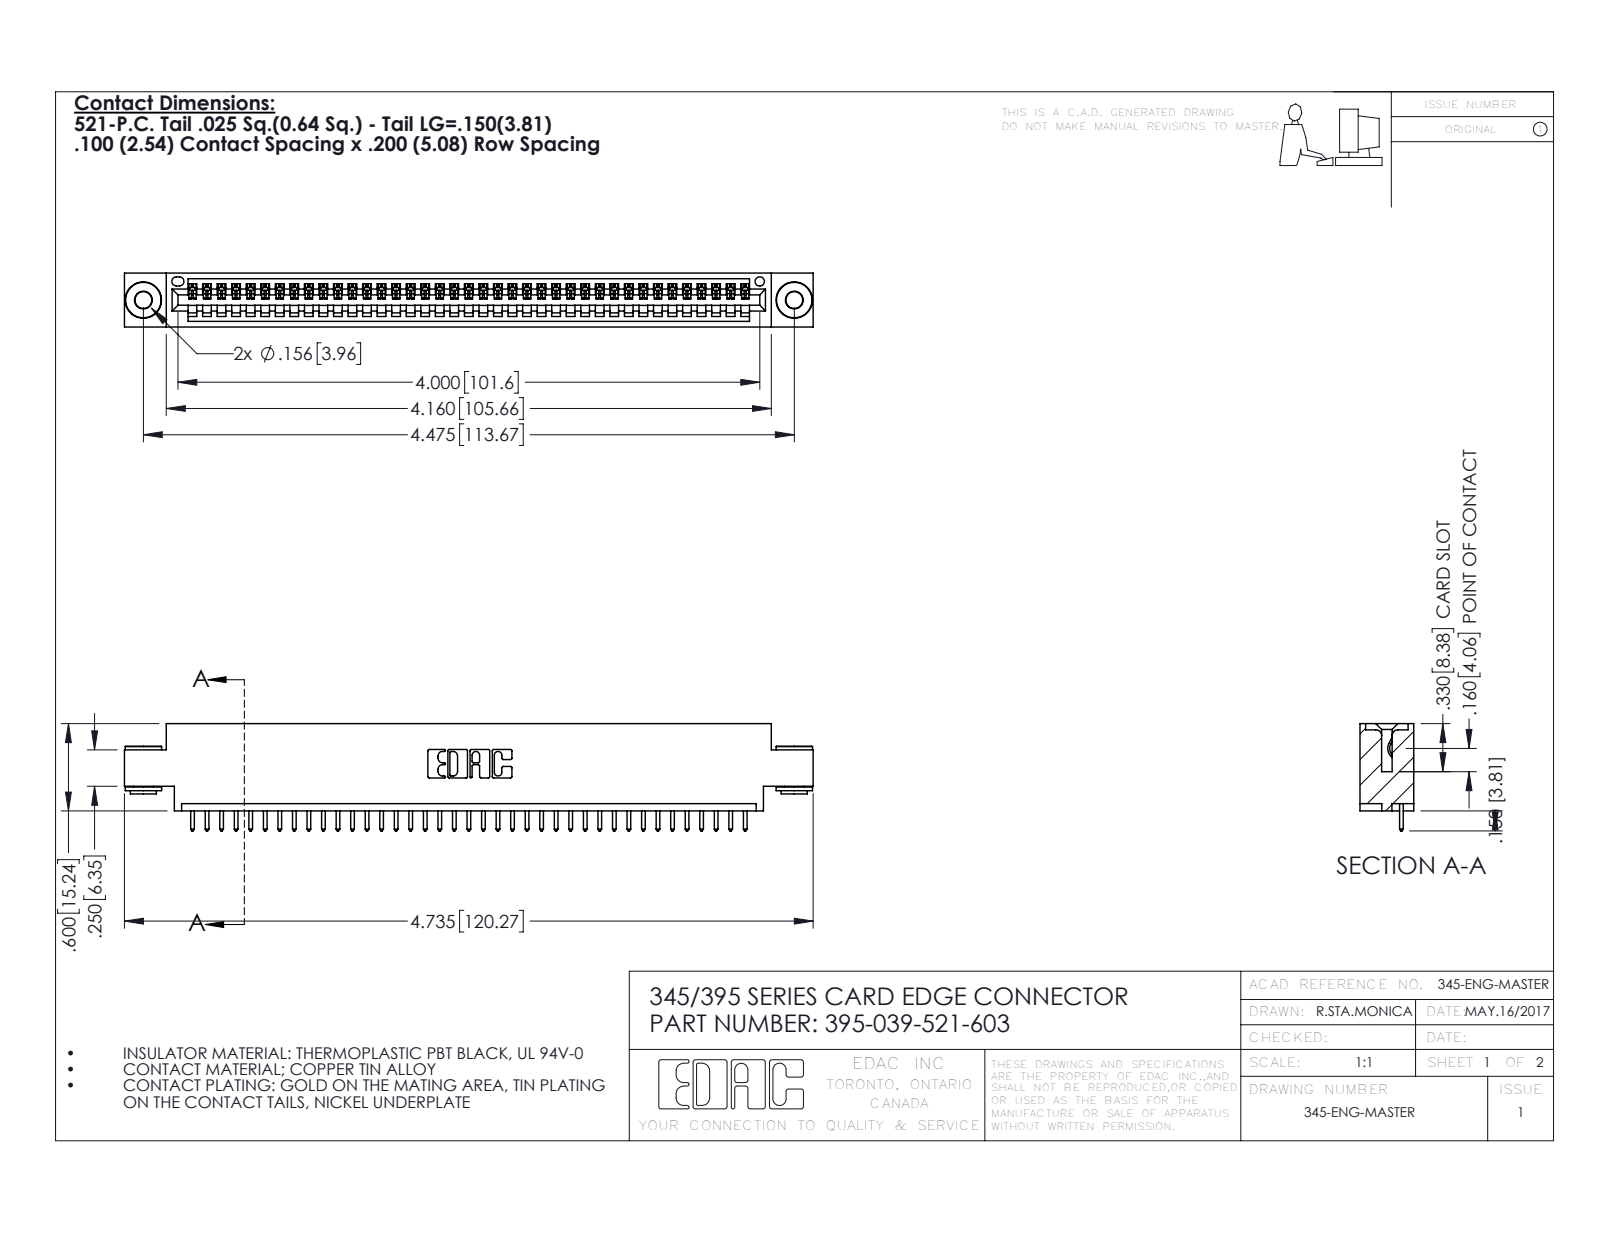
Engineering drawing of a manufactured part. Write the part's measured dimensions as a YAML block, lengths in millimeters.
part_name: "395-039-521-603; 345 Part_0.170 Offset - 0.156 Dia-TH; 345-292-001_345-293-121; 345-250-002_345-250-002-102"
step_written_by: "SolidWorks 2016 (CONFIG_CONTROL_DESIGN)"
units: millimeters
bodies: {solids: 42, faces: 2430, planar: 1654, cylindrical: 768, other: 8}
overall_size: [120.3, 18.7, 9.4]
volume: 11200
surface_area: 14740
round_holes:
  - {diameter: 2.9, count: 2}
  - {diameter: 4, count: 2}
  - {diameter: 1.6, count: 1}
round_bosses_or_shafts:
  - {diameter: 6.4, count: 2}
  - {diameter: 4.6, count: 2}
  - {diameter: 3.5, count: 2}
partial_cylinders:
  - {radius: 0.2, count: 78}
  - {radius: 0.3, count: 78}
  - {radius: 0.3, count: 22}
  - {radius: 0.2, count: 6}
  - {radius: 0.8, count: 6}
  - {radius: 0.7, count: 3}
  - {radius: 0.8, count: 2}
  - {radius: 1, count: 2}
face_to_face_distances: [1.8, 7.6, 9.4, 5.1, 2.5, 6.9, 0.6, 5.7, 4.4, 3.8]
hole_center_spacings: [6.9, 107.7, 113.7]
